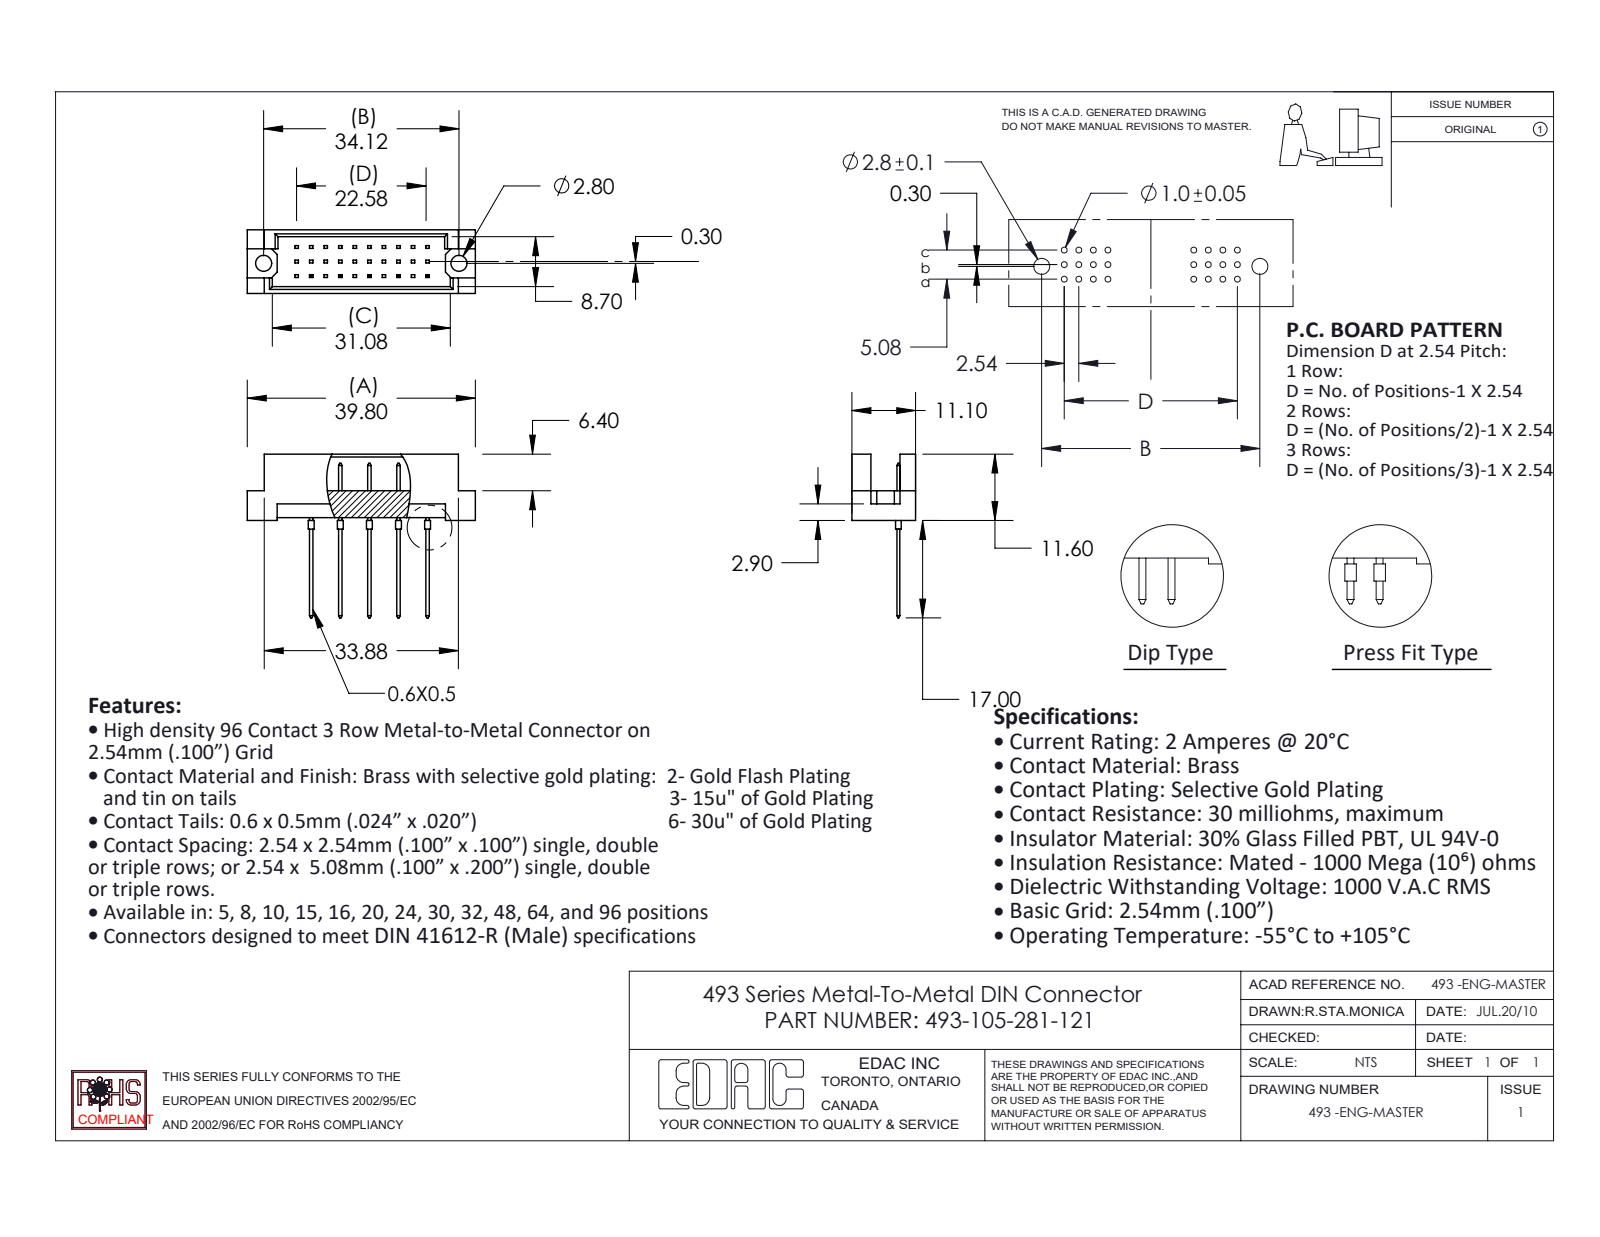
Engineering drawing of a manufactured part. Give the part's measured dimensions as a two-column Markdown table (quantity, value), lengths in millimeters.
| quantity | value |
| --- | --- |
| part name | 493-105-281-121; 493-290_81; 493 Part_30 |
| STEP written by | SolidWorks 2020 (CONFIG_CONTROL_DESIGN) |
| units | millimeters |
| bodies | 6 solids, 282 faces (268 planar, 14 cylindrical, 0 other) |
| overall size | 39.8 × 28.6 × 11.1 |
| volume | 2 417 mm³ |
| surface area | 3 045 mm² |
| round holes (diameter × count) | 2.8 × 2 |
| round bosses / shafts (diameter × count) | 1 × 5 |
| main face-to-face distances | 1.2, 9.9, 11.1, 8.7, 0.5, 5.08, 4.7, 2.4, 2.76, 8.34 |
| hole center spacings | 34.12 |
